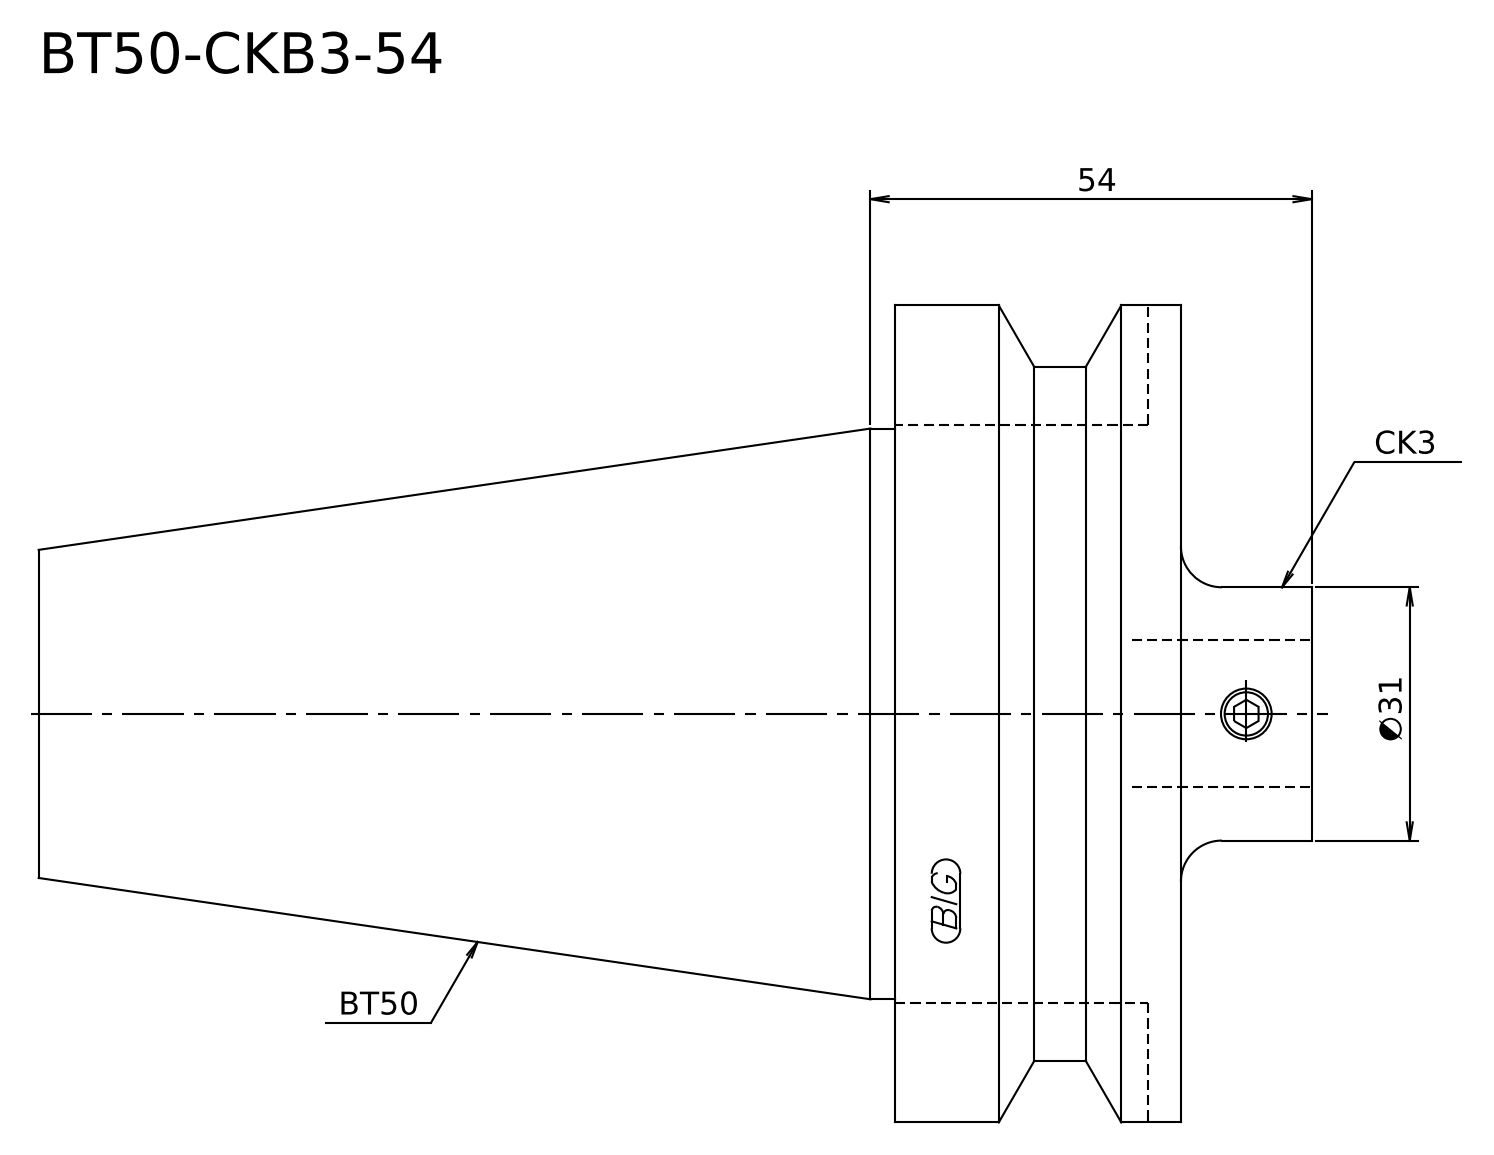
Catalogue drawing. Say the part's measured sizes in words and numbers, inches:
Its 3-D file was written by "Kubotek KeyCreator V8.5.1 (14335) (CONFIG_CONTROL_DESIGN)". It is 1 solid with 13 faces: 4 planar, 5 cylindrical and 4 other. Overall it measures 6.134 by 3.937 by 3.937 inches. Its volume is 31.98 cubic inches and its surface area 71.13 square inches. Round bosses or shafts: 1 of diameter 3.937, 1 of diameter 3.346, 1 of diameter 2.75, 1 of diameter 1.22. The main face-to-face distances are 1.378, 5.504, 4.126, 0.63, 2.008, 6.134.
